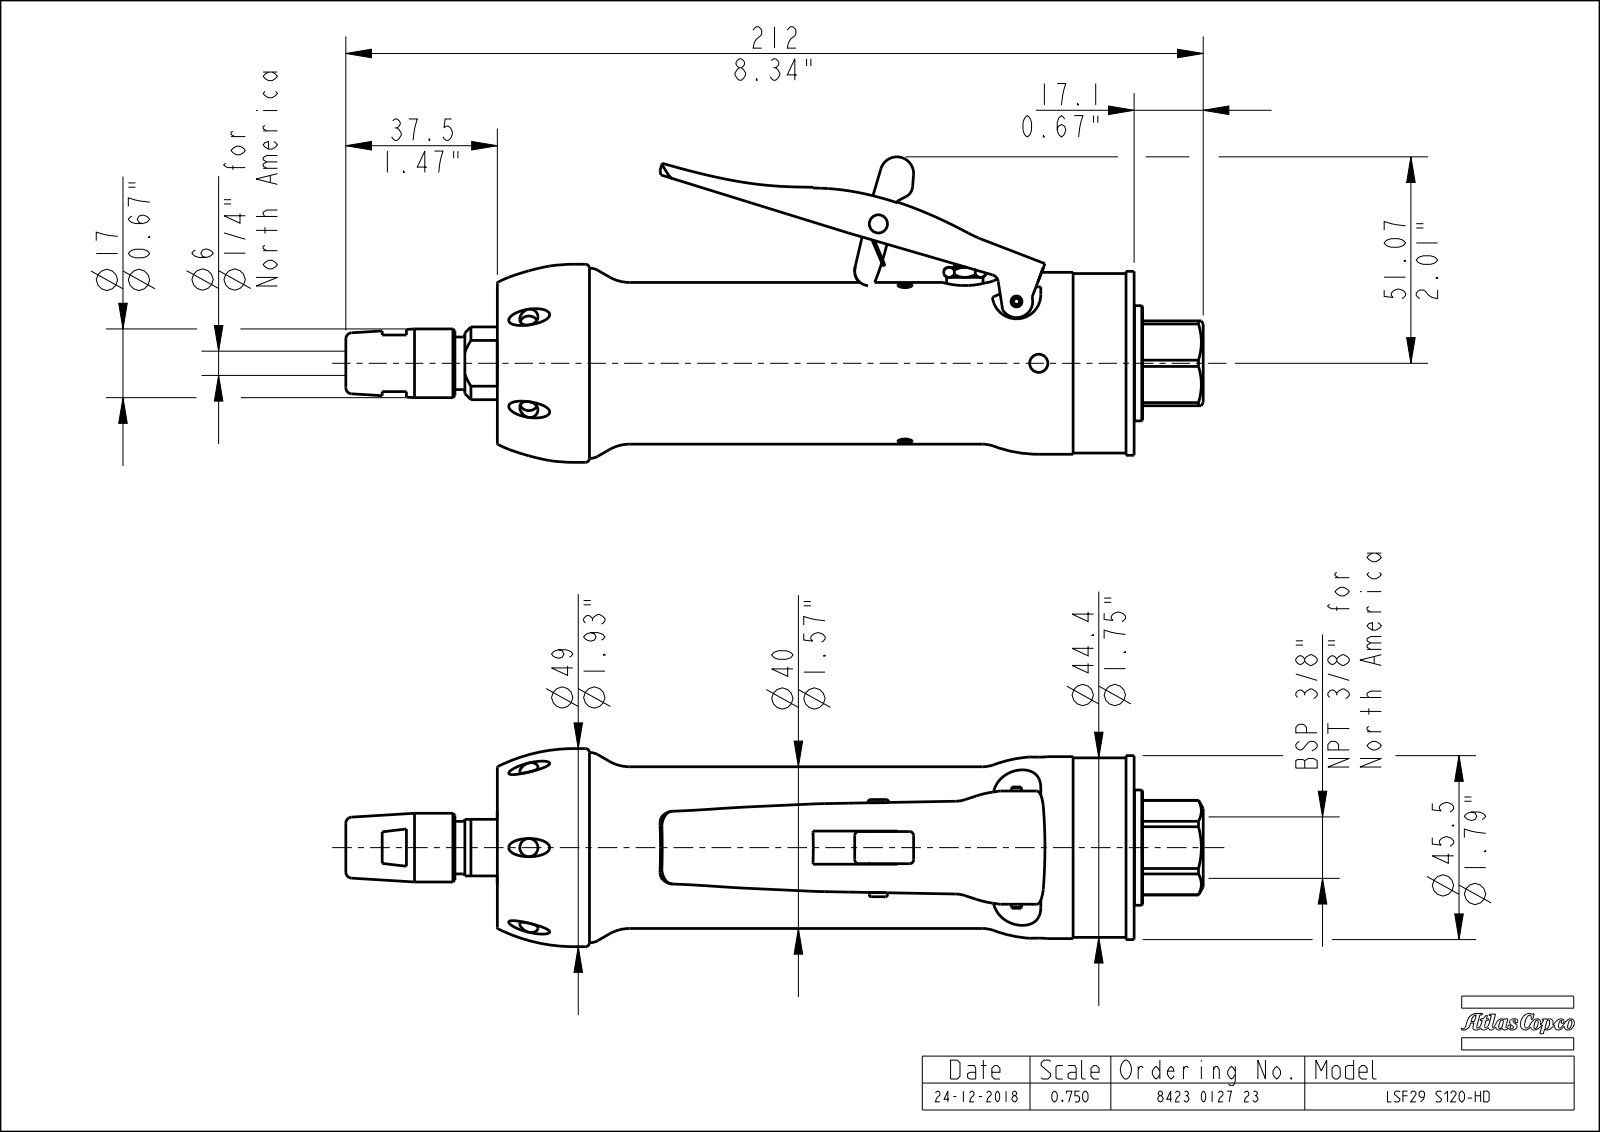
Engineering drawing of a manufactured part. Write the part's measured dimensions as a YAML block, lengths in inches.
part_name: "EXT_COMP_SW0016"
step_written_by: "CREO PARAMETRIC BY PTC INC, 2018100 (CONFIG_CONTROL_DESIGN)"
units: inches
bodies: {solids: 2, faces: 762, planar: 155, cylindrical: 244, other: 363}
overall_size: [8.354, 2.975, 1.929]
volume: 13.94
surface_area: 76.15
round_holes:
  - {diameter: 0.094, count: 8}
  - {diameter: 0.1, count: 8}
  - {diameter: 0.177, count: 4}
  - {diameter: 0.138, count: 2}
  - {diameter: 0.059, count: 1}
  - {diameter: 0.098, count: 1}
  - {diameter: 0.106, count: 1}
  - {diameter: 0.122, count: 1}
  - {diameter: 0.157, count: 1}
  - {diameter: 0.236, count: 1}
  - {diameter: 0.323, count: 1}
  - {diameter: 0.433, count: 1}
round_bosses_or_shafts:
  - {diameter: 0.098, count: 3}
  - {diameter: 0.02, count: 3}
  - {diameter: 1.929, count: 1}
  - {diameter: 1.85, count: 1}
  - {diameter: 1.791, count: 1}
  - {diameter: 1.772, count: 1}
  - {diameter: 1.748, count: 1}
  - {diameter: 1.693, count: 1}
partial_cylinders:
  - {radius: 0.039, count: 14}
  - {radius: 0.157, count: 3}
  - {radius: 0.079, count: 2}
  - {radius: 0.059, count: 1}
  - {radius: 0.118, count: 1}
  - {radius: 0.163, count: 1}
  - {radius: 0.167, count: 1}
  - {radius: 0.217, count: 1}
face_to_face_distances: [0.059, 6.004, 0.827, 5.612, 0.392, 5.736, 0.124, 0.268, 5.677, 0.065]
hole_center_spacings: [0.422, 0.551, 0.78, 1.019, 1.102, 0.845, 3.671, 0.417]
